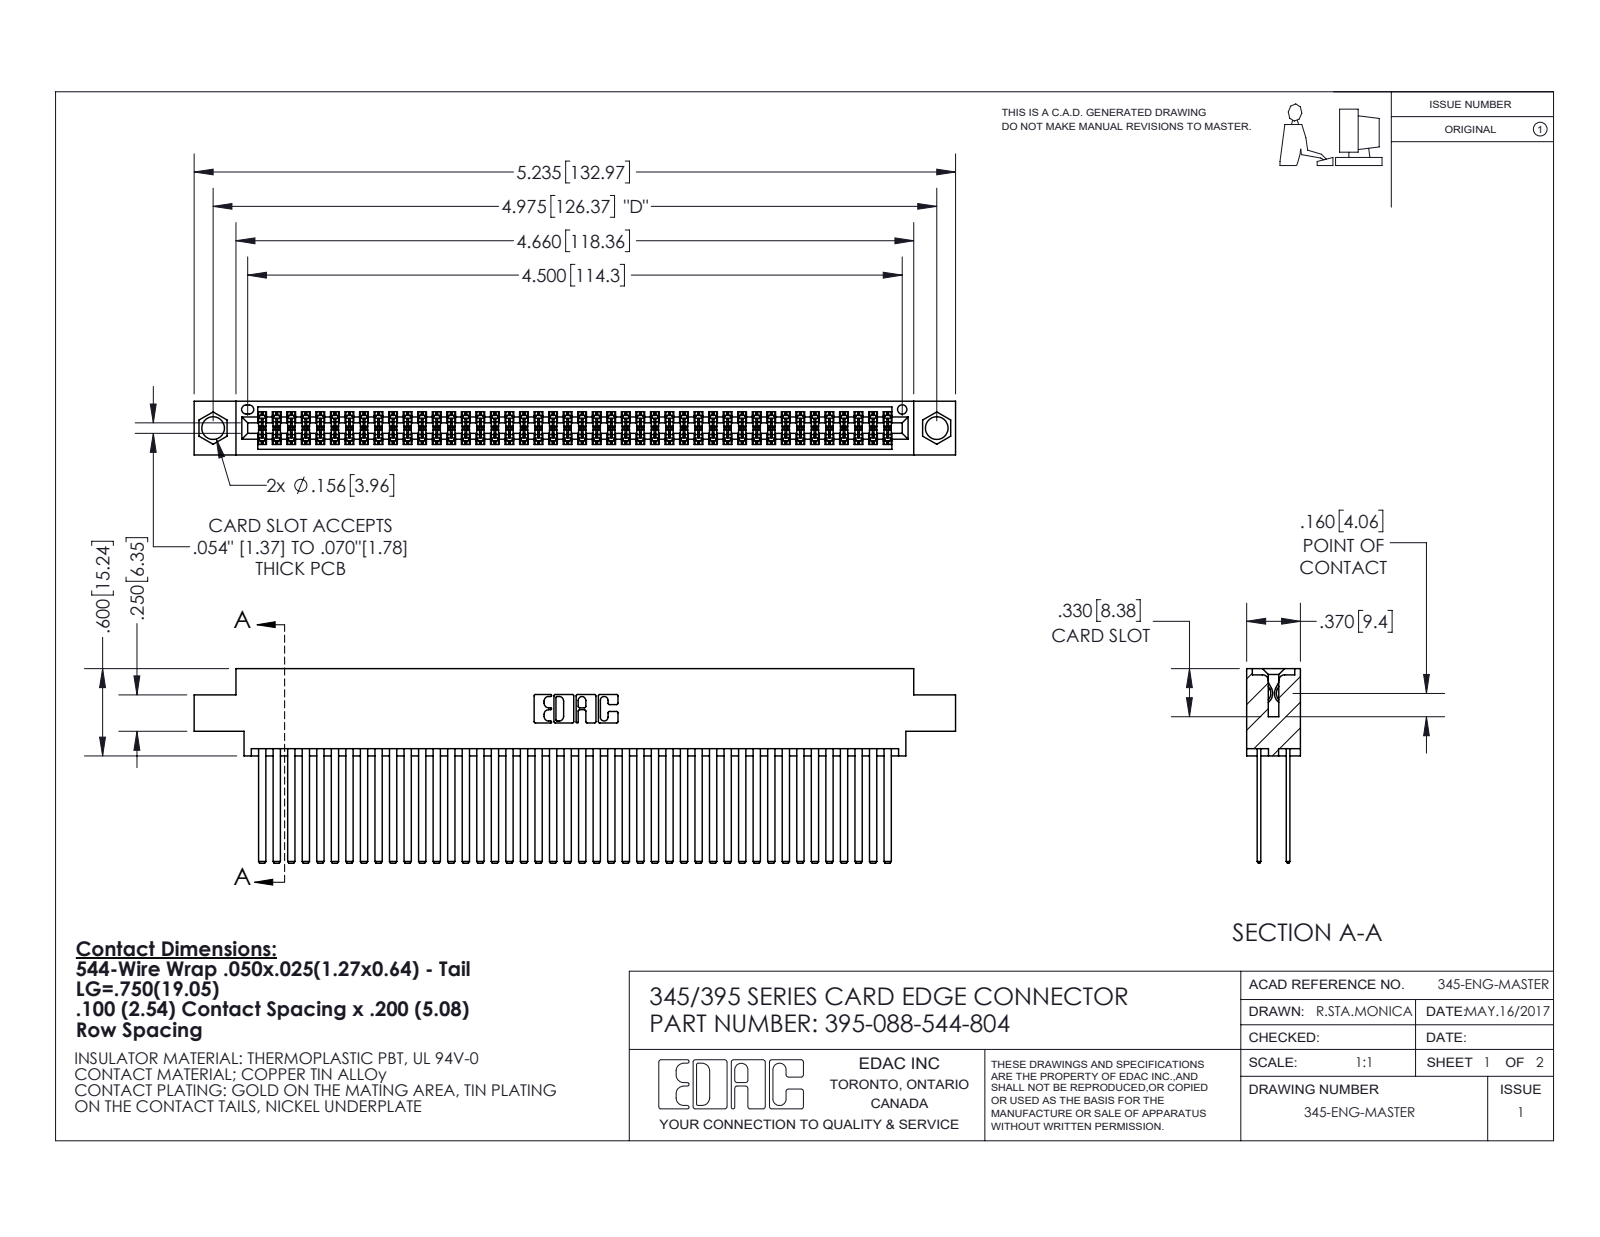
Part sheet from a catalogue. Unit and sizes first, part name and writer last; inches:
Units: inches
Overall size (bounding box): 5.235 × 1.337 × 0.37
Round holes (diameter × count): ⌀0.156 ×2, ⌀0.064 ×1
Partial cylindrical surfaces — rounded edges, fillets, slot ends (radius × count): R0.006 ×132, R0.01 ×22, R0.007 ×6, R0.031 ×6, R0.026 ×3, R0.014 ×2, R0.019 ×2, R0.022 ×2
Main face-to-face distances: 0.2, 0.025, 0.072, 0.098, 0.272, 0.298, 0.225, 0.175, 0.37, 0.15
Hole centre spacings: 0.27, 4.739, 4.975
Volume: 0.851 in³ · Surface area: 37.62 in²
Bodies: 89 solids, 4016 faces (2650 planar, 1366 cylindrical, 0 other)
Part name (STEP PRODUCT): 345 Part_0.170 Offset - 0.156 Dia-TI; 395-088-544-804; 345-292-001_345-293-144
STEP written by: SolidWorks 2020 (CONFIG_CONTROL_DESIGN)
